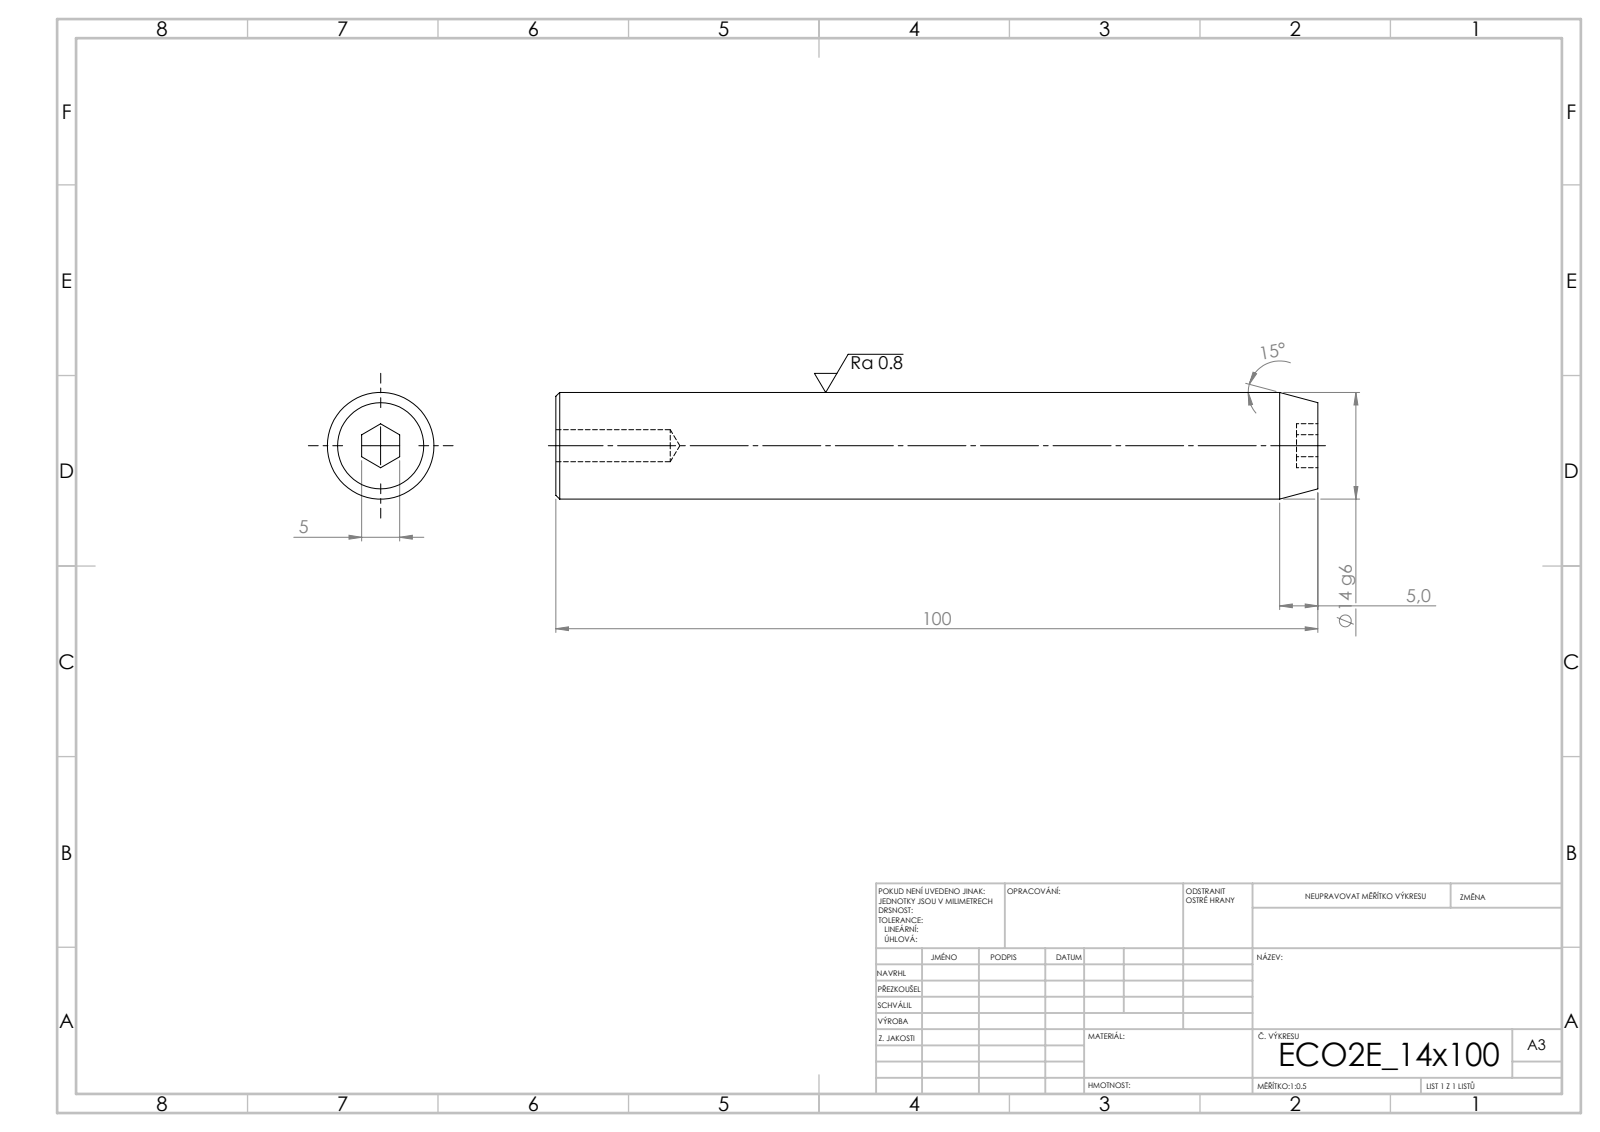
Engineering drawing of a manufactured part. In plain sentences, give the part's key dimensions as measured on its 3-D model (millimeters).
Its 3-D file was written by "SolidWorks 2019 (CONFIG_CONTROL_DESIGN)". It is 1 solid with 19 faces: 9 planar, 4 cylindrical and 6 other. Overall it measures 100 by 14 by 14 millimeters. Its volume is 14 976 cubic millimeters and its surface area 4 874 square millimeters. Round holes: 1 of diameter 4.2. Round bosses or shafts: 1 of diameter 14. The main face-to-face distances are 100, 5, 2.8, 97.2.
